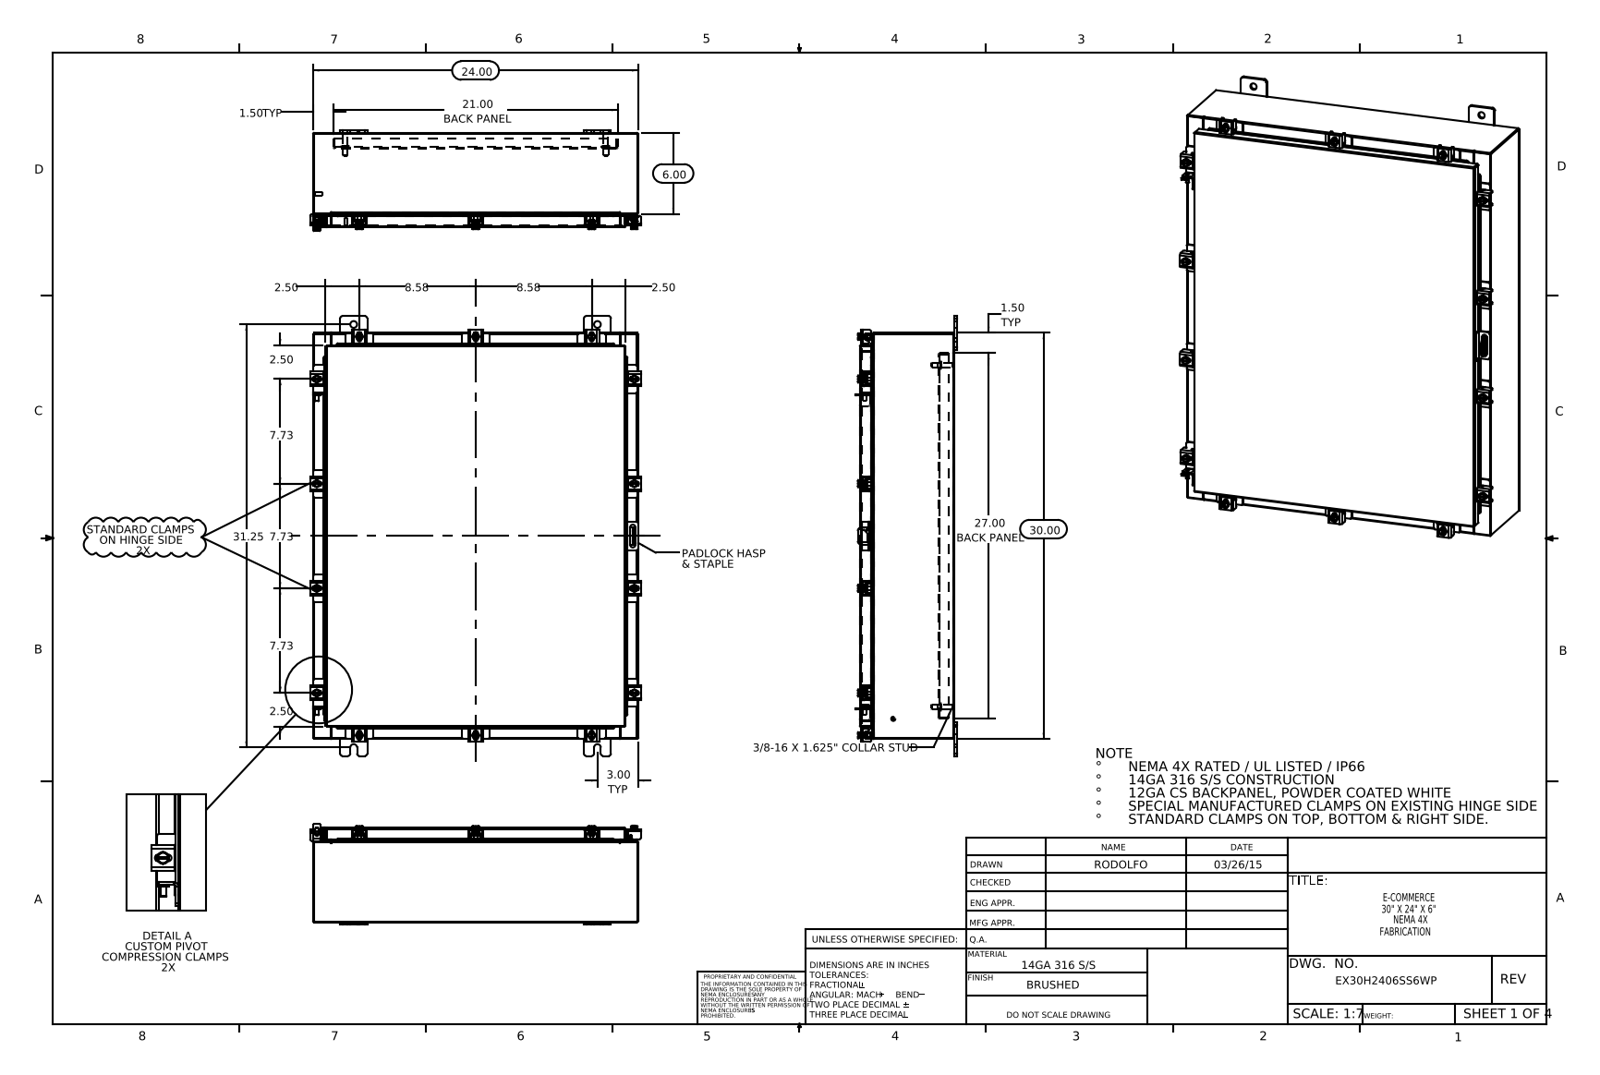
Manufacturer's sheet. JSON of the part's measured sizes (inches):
{"part_name": "HW-CLN-NH-20330; N-WMT04X30402202210-00 22101002; ATEX CLAMP HINGE BRAKET; EX30H2406SS6WP Body (+8 more)", "step_written_by": "SolidWorks 2014 (CONFIG_CONTROL_DESIGN)", "units": "inches", "bodies": {"solids": 91, "faces": 2272, "planar": 1211, "cylindrical": 885, "other": 176}, "overall_size": [32.5, 24.421, 7.453], "volume_in3": 248.6, "surface_area_in2": 6142, "round_holes": [[0.213, 14], [0.26, 14], [0.5, 8], [0.125, 1], [0.25, 1]], "round_bosses_or_shafts": [[0.5, 14], [0.25, 14], [0.399, 12], [0.625, 4], [0.375, 4], [0.33, 4], [0.315, 2], [0.236, 2]], "partial_cylinders_radius": [[0.06, 62], [0.141, 28], [0.013, 26], [0.12, 26], [0.19, 24], [0.088, 22], [0.09, 20], [0.05, 19]], "face_to_face_distances": [0.075, 6.9, 6.975, 6.826, 0.104, 1, 1.075, 5.826, 5.9, 1.179], "hole_center_spacings": [2.347, 4.44, 20.544, 23.451, 24.31, 26.507, 27.37, 32.286]}
